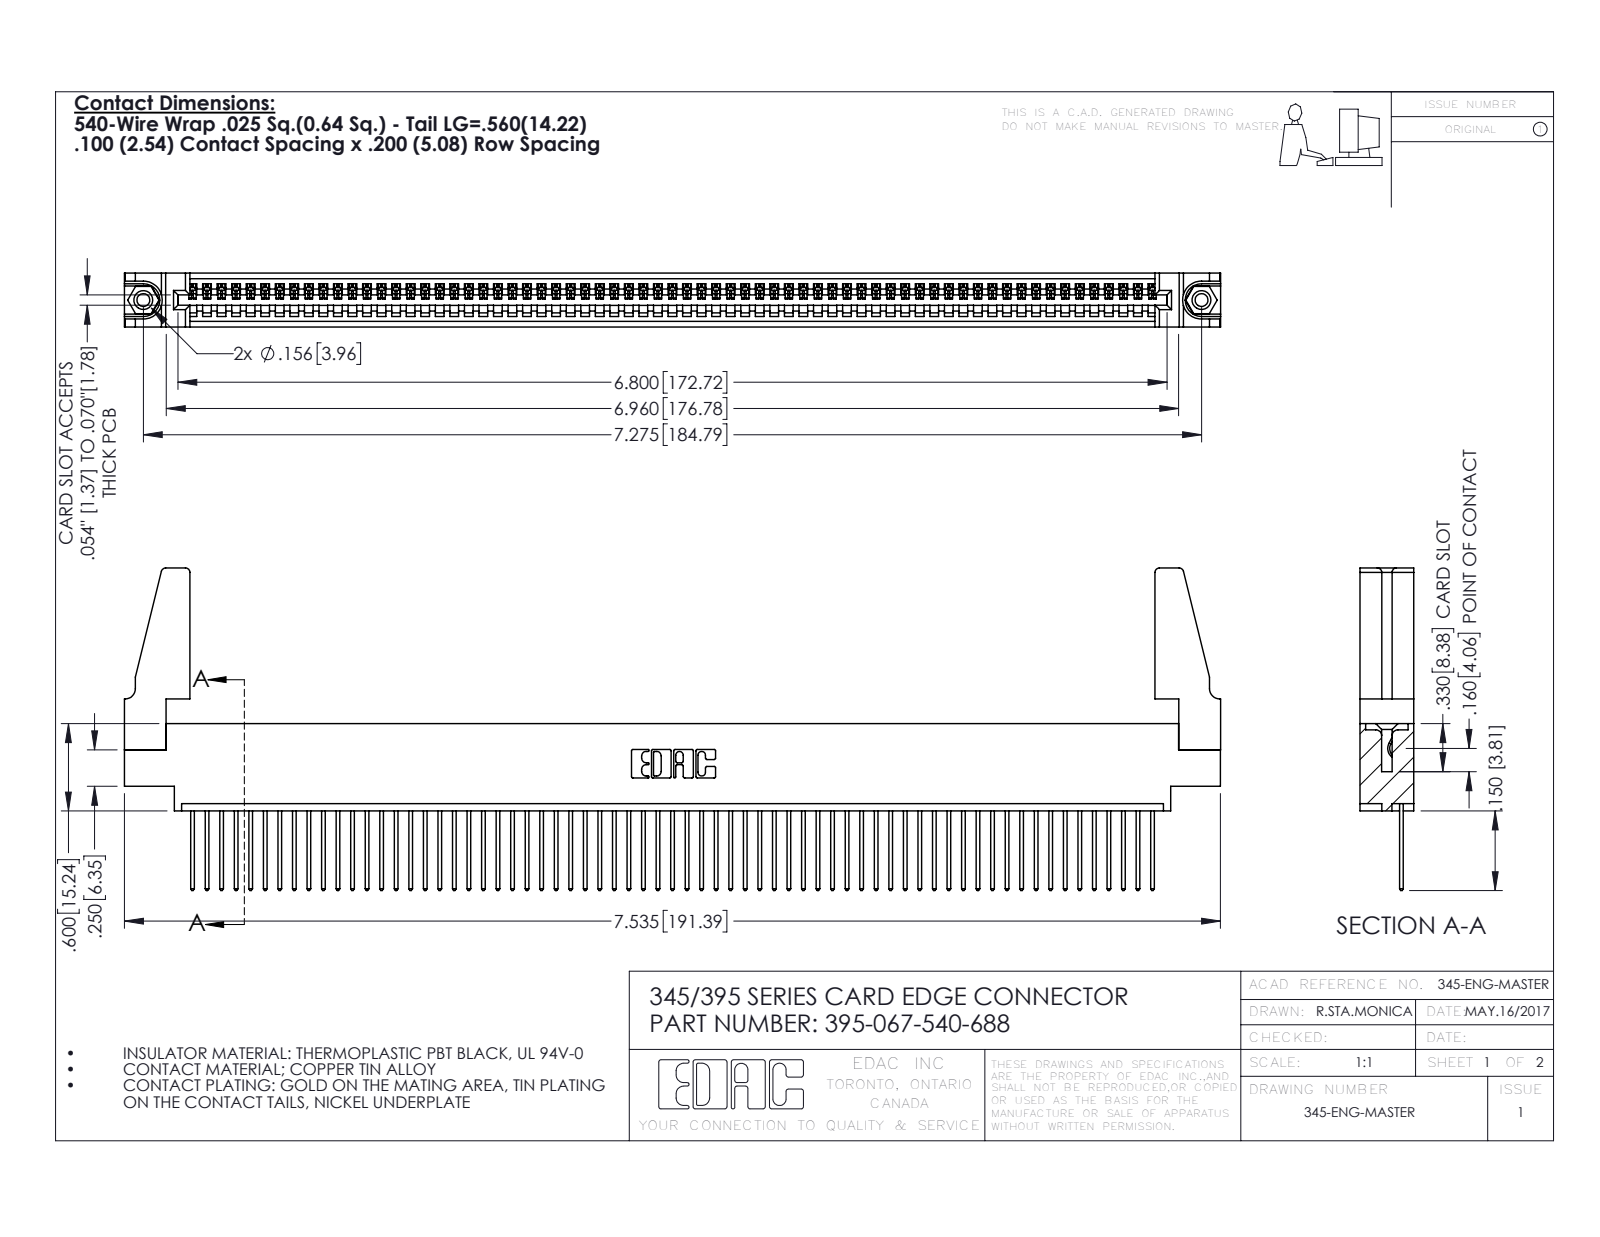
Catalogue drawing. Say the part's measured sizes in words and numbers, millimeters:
The part is named "345-250-001_345-250-001-102; 395-067-540-688; 345-292-001_345-293-140; 345-220-078_345-220-088 (+1 more)". Its 3-D file was written by "SolidWorks 2016 (CONFIG_CONTROL_DESIGN)". It is 72 solids with 4140 faces: 2836 planar, 1288 cylindrical and 16 other. Overall it measures 191.4 by 56.3 by 9.4 millimeters. Its volume is 21 610 cubic millimeters and its surface area 28 650 square millimeters. Round holes: 2 of diameter 2.3, 2 of diameter 3.2, 2 of diameter 4, 1 of diameter 1.6. Round bosses or shafts: 2 of diameter 3.9. Partial cylindrical surfaces (rounded edges, fillets, slot ends): 134 of radius 0.2, 134 of radius 0.3, 22 of radius 0.3, 8 of radius 0.8, 6 of radius 0.2, 6 of radius 0.8, 3 of radius 0.7, 2 of radius 0.8. The main face-to-face distances are 1.8, 7.6, 9.4, 2.5, 6.9, 0.6, 5.1, 5.7, 4.4, 3.8. The hole center spacings are 6.9, 178.8, 184.8.
